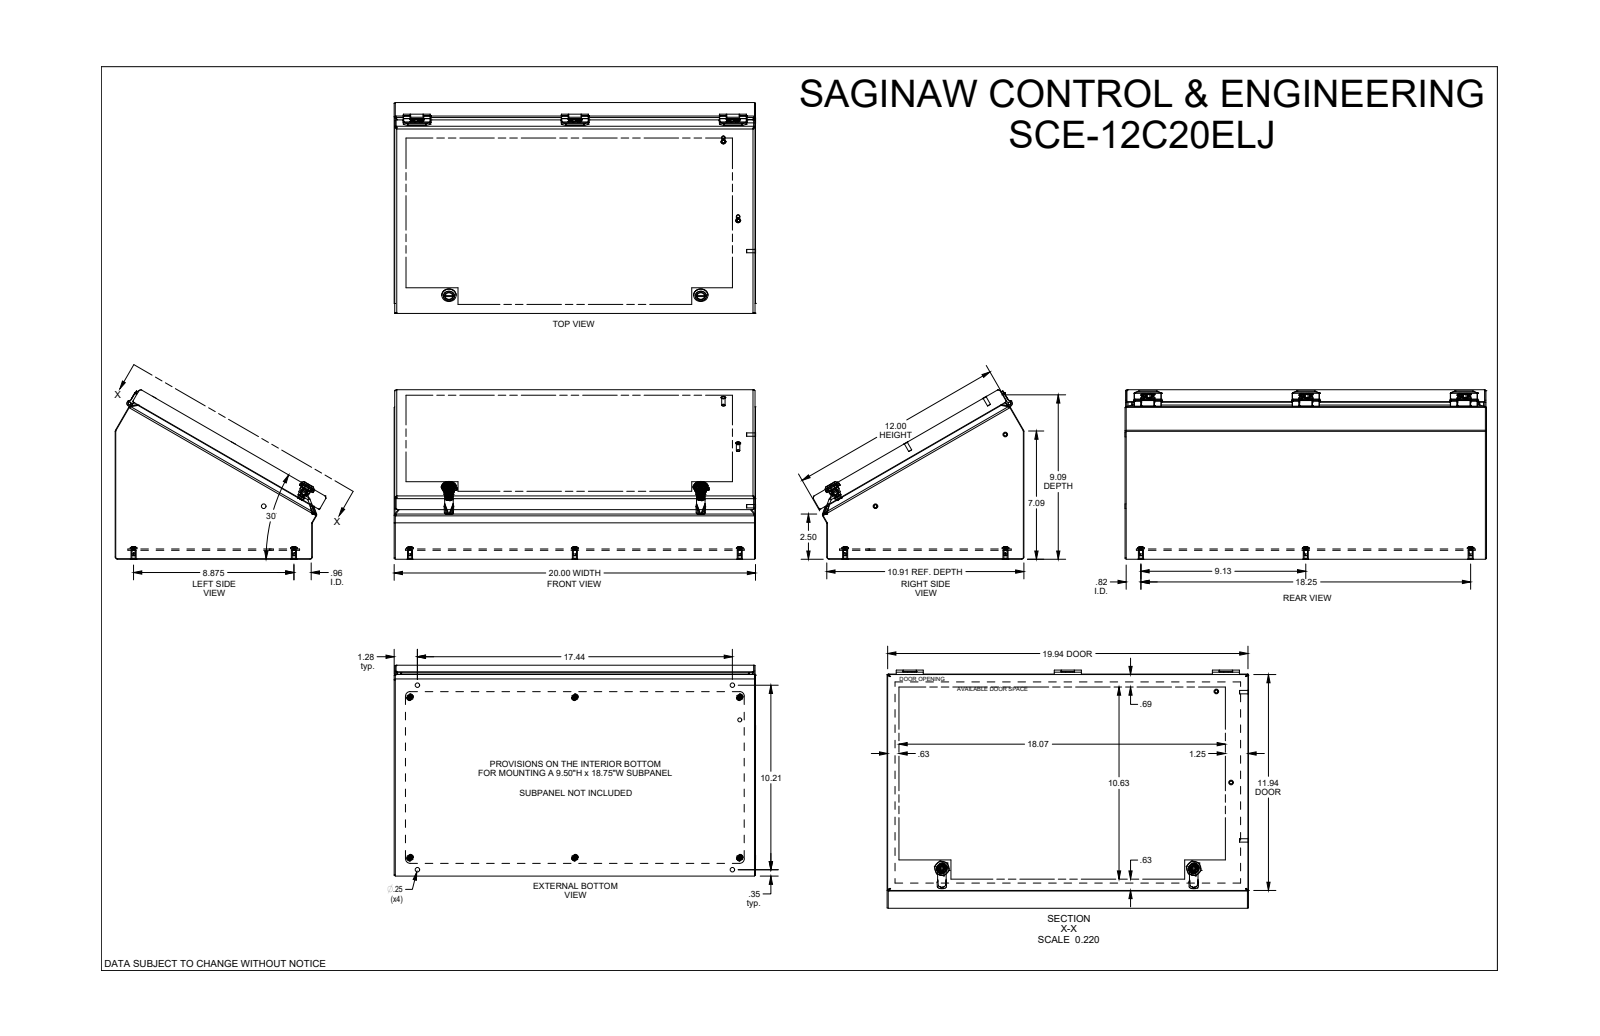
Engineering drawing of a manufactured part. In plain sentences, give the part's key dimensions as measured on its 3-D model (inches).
The part is named "SCE-12C20ELJ". Its 3-D file was written by "SolidWorks 2019 (AUTOMOTIVE_DESIGN)". It is 37 solids with 1372 faces: 535 planar, 557 cylindrical and 280 other. Overall it measures 20.004 by 11.665 by 9.38 inches. Its volume is 73.37 cubic inches and its surface area 2 295 square inches. Round holes: 10 of diameter 0.25, 6 of diameter 0.19, 6 of diameter 0.281, 4 of diameter 0.193, 3 of diameter 0.02, 3 of diameter 0.1, 3 of diameter 0.174, 3 of diameter 0.266, 2 of diameter 0.2, 2 of diameter 0.239, 2 of diameter 0.254, 2 of diameter 0.269. Round bosses or shafts: 6 of diameter 0.28, 4 of diameter 0.256, 4 of diameter 0.188, 3 of diameter 0.26, 3 of diameter 0.18, 2 of diameter 0.788, 2 of diameter 0.548, 2 of diameter 0.46. Partial cylindrical surfaces (rounded edges, fillets, slot ends): 36 of radius 0.03, 31 of radius 0.013, 24 of radius 0.06, 22 of radius 0.01, 22 of radius 0.015, 16 of radius 0.12, 13 of radius 0.02, 9 of radius 0.062. The main face-to-face distances are 0.06, 0.06, 0.436, 0.496, 0.075, 0.511, 0.571, 19.94, 10.846, 19.88. The hole center spacings are 0.78, 8.744, 8.75, 9.125, 9.549, 12.729, 12.924, 13.94.
